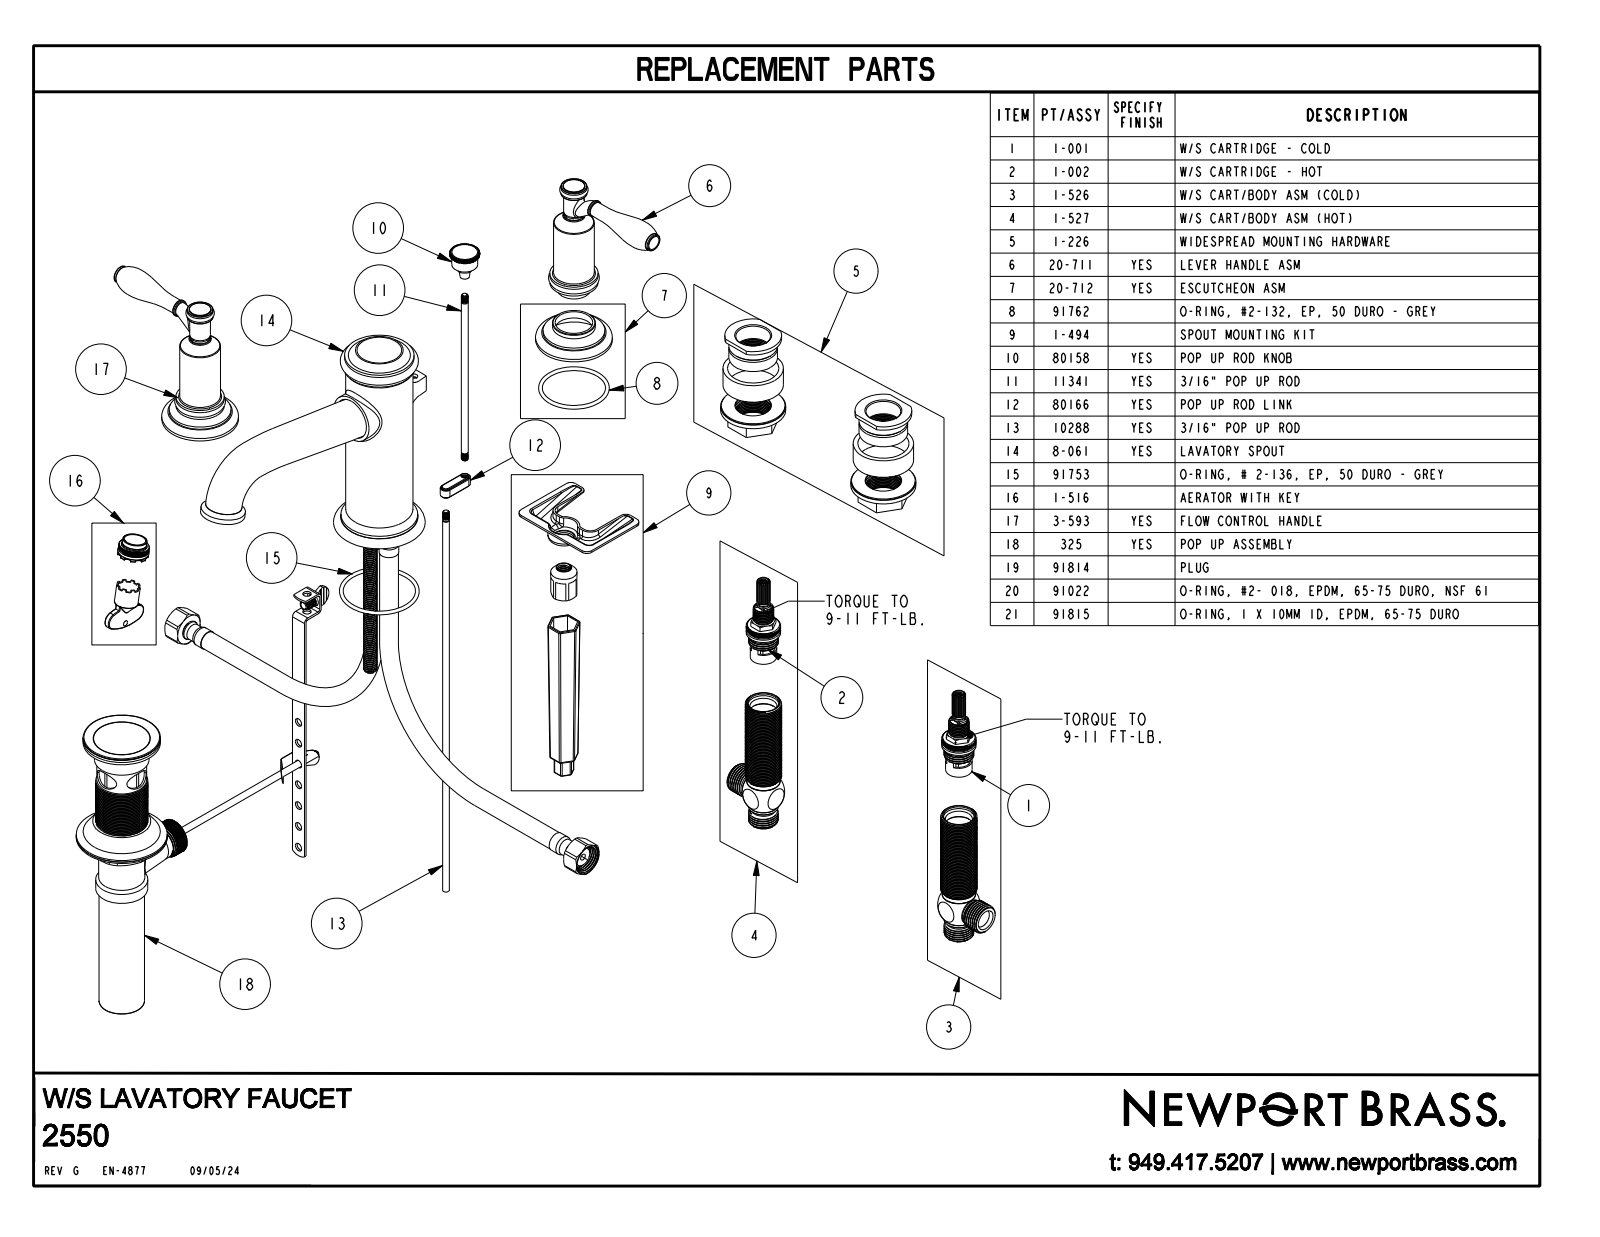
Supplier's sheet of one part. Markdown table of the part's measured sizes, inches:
| quantity | value |
| --- | --- |
| part name | 2550 |
| STEP written by | CREO PARAMETRIC BY PTC INC, 2018400 (CONFIG_CONTROL_DESIGN) |
| units | inches |
| bodies | 3 solids, 987 faces (267 planar, 294 cylindrical, 426 other) |
| overall size | 14.3 × 8.461 × 6.308 |
| volume | 30.96 in³ |
| surface area | 122.8 in² |
| round holes (diameter × count) | 0.694 × 1 |
| round bosses / shafts (diameter × count) | 2.11 × 3, 1.12 × 3, 1.7 × 2, 1.33 × 2, 0.714 × 2, 0.6 × 2, 0.57 × 2, 0.42 × 2 |
| partial cylindrical surfaces (radius × count) | 0.01 × 90, 0.005 × 64, 0.02 × 4, 0.04 × 2, 0.24 × 2, 0.125 × 1, 0.155 × 1, 0.195 × 1 |
| main face-to-face distances | 0.39, 0.45, 0.75, 0.3, 5.627, 5.177, 4.877, 0.5, 0.04, 0.35 |
